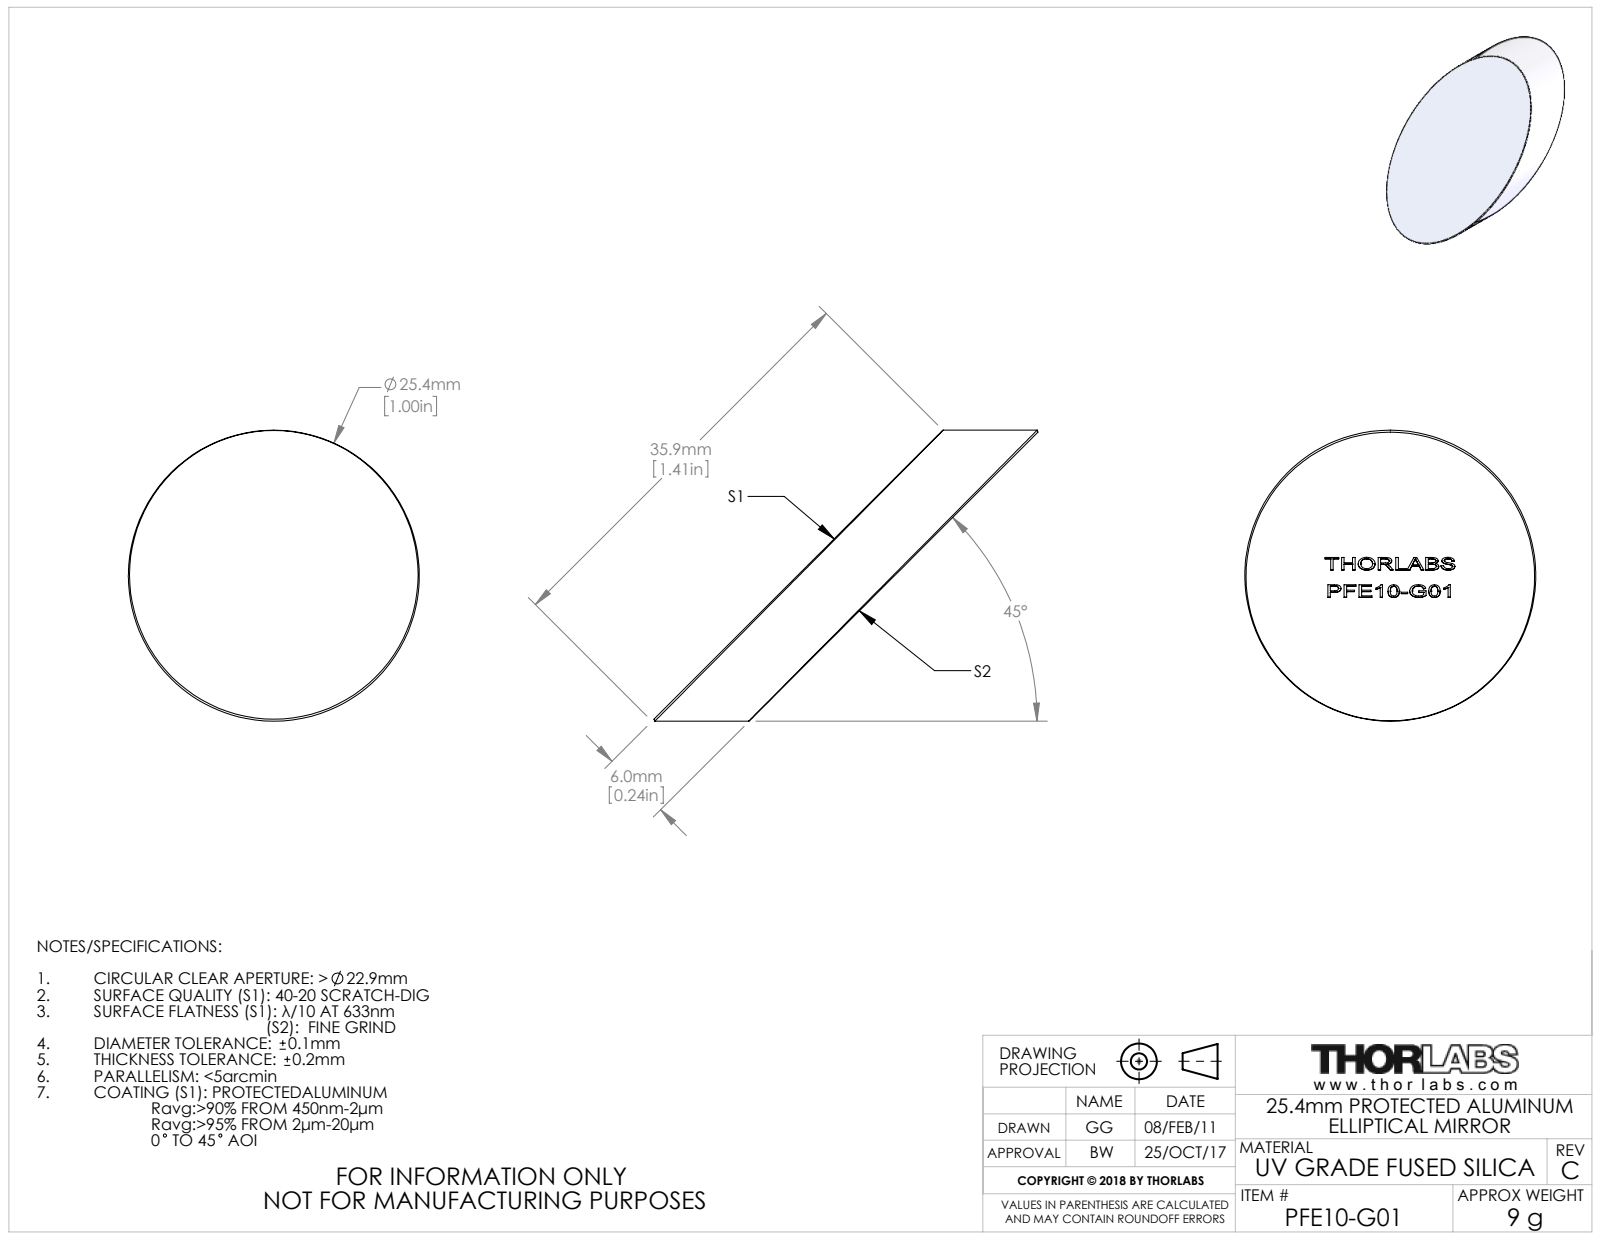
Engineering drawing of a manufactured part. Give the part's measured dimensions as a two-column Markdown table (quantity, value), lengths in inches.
| quantity | value |
| --- | --- |
| part name | 21936-E0W |
| STEP written by | SolidWorks 2016 (CONFIG_CONTROL_DESIGN) |
| units | inches |
| bodies | 1 solid, 223 faces (136 planar, 2 cylindrical, 85 other) |
| overall size | 1.32 × 1 × 1 |
| volume | 0.262 in³ |
| surface area | 3.241 in² |
| round bosses / shafts (diameter × count) | 1 × 1 |
| main face-to-face distances | 0.236, 0.133, 0.061, 0.054, 0.14, 0.079, 0.046, 0.233, 0.163, 0.186 |
